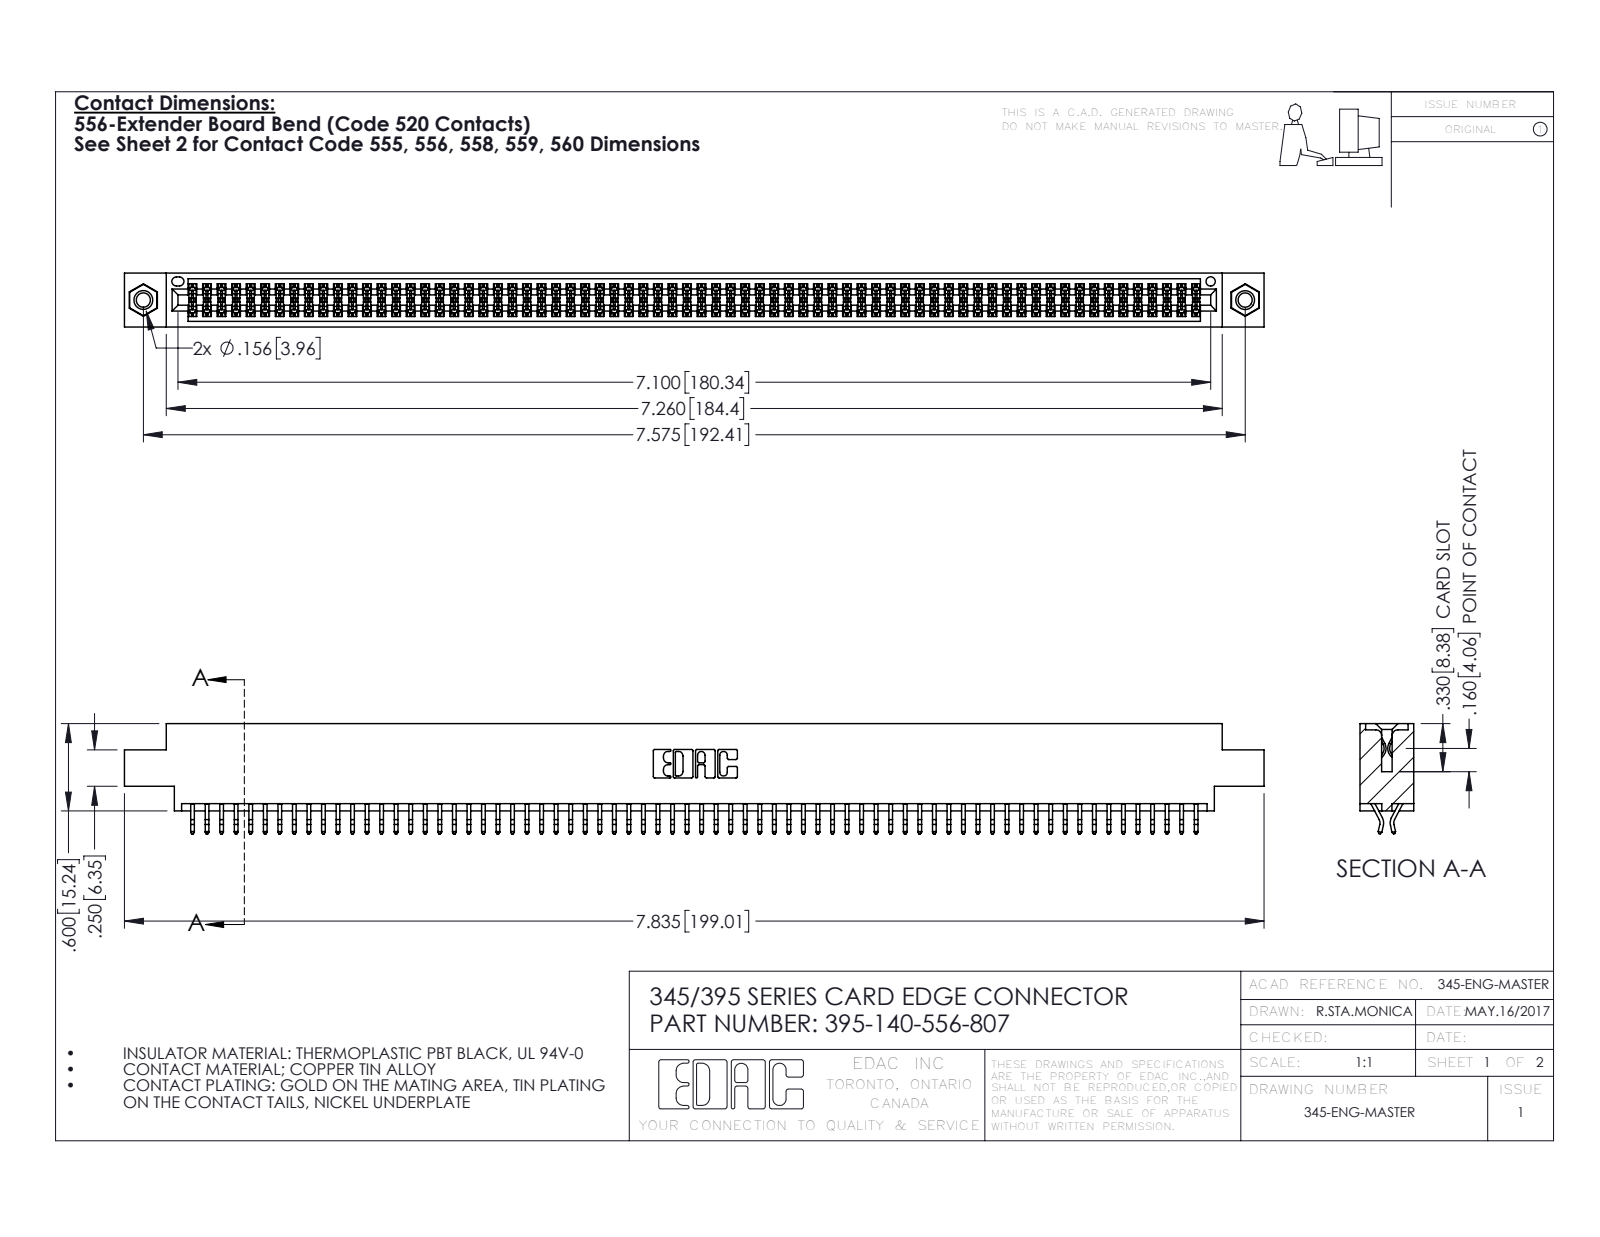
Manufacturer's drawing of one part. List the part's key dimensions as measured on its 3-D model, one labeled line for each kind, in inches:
Part name (STEP PRODUCT): 345-292-001_556 Tail; 345-250-001_345-250-005-103; 345 Part_0.170 Offset - 0.156 Dia-TI; 395-140-556-807
STEP written by: SolidWorks 2016 (CONFIG_CONTROL_DESIGN)
Units: inches
Bodies: 143 solids, 8030 faces (5296 planar, 2718 cylindrical, 16 other)
Overall size (bounding box): 7.835 × 0.757 × 0.37
Volume: 1.187 in³ · Surface area: 45.5 in²
Round holes (diameter × count): ⌀0.098 ×2, ⌀0.125 ×2, ⌀0.156 ×2, ⌀0.064 ×1
Round bosses / shafts (diameter × count): ⌀0.155 ×2
Partial cylindrical surfaces — rounded edges, fillets, slot ends (radius × count): R0.006 ×210, R0.01 ×22, R0.007 ×6, R0.031 ×6, R0.026 ×3, R0.01 ×2, R0.014 ×2, R0.019 ×2
Main face-to-face distances: 0.072, 0.298, 0.37, 0.2, 0.025, 0.098, 0.272, 0.225, 0.175, 0.149
Hole centre spacings: 0.27, 7.339, 7.575
